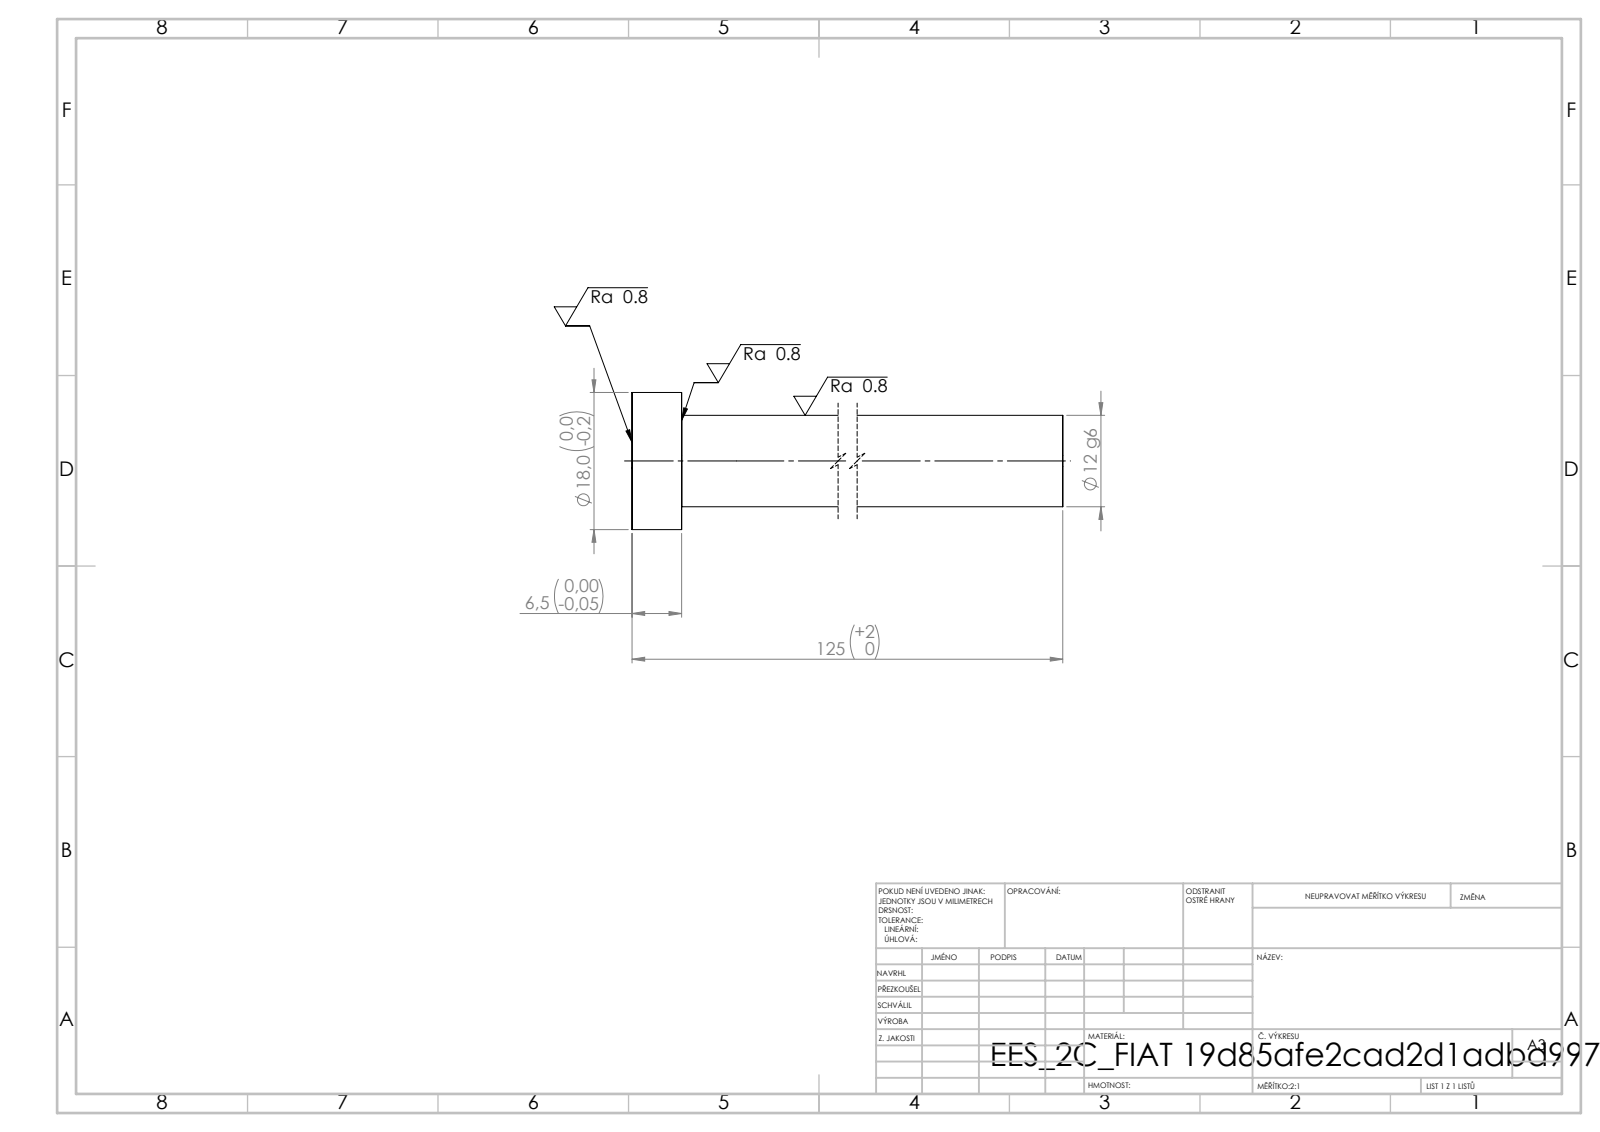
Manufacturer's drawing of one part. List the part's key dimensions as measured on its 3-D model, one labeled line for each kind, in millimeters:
STEP written by: SolidWorks 2019 (CONFIG_CONTROL_DESIGN)
Units: millimetres
Bodies: 1 solid, 7 faces (3 planar, 4 cylindrical, 0 other)
Overall size (bounding box): 125 × 18 × 18
Volume: 15 056 mm³ · Surface area: 5 344 mm²
Round bosses / shafts (diameter × count): ⌀18 ×1, ⌀12 ×1
Main face-to-face distances: 6.5, 125, 118.5
